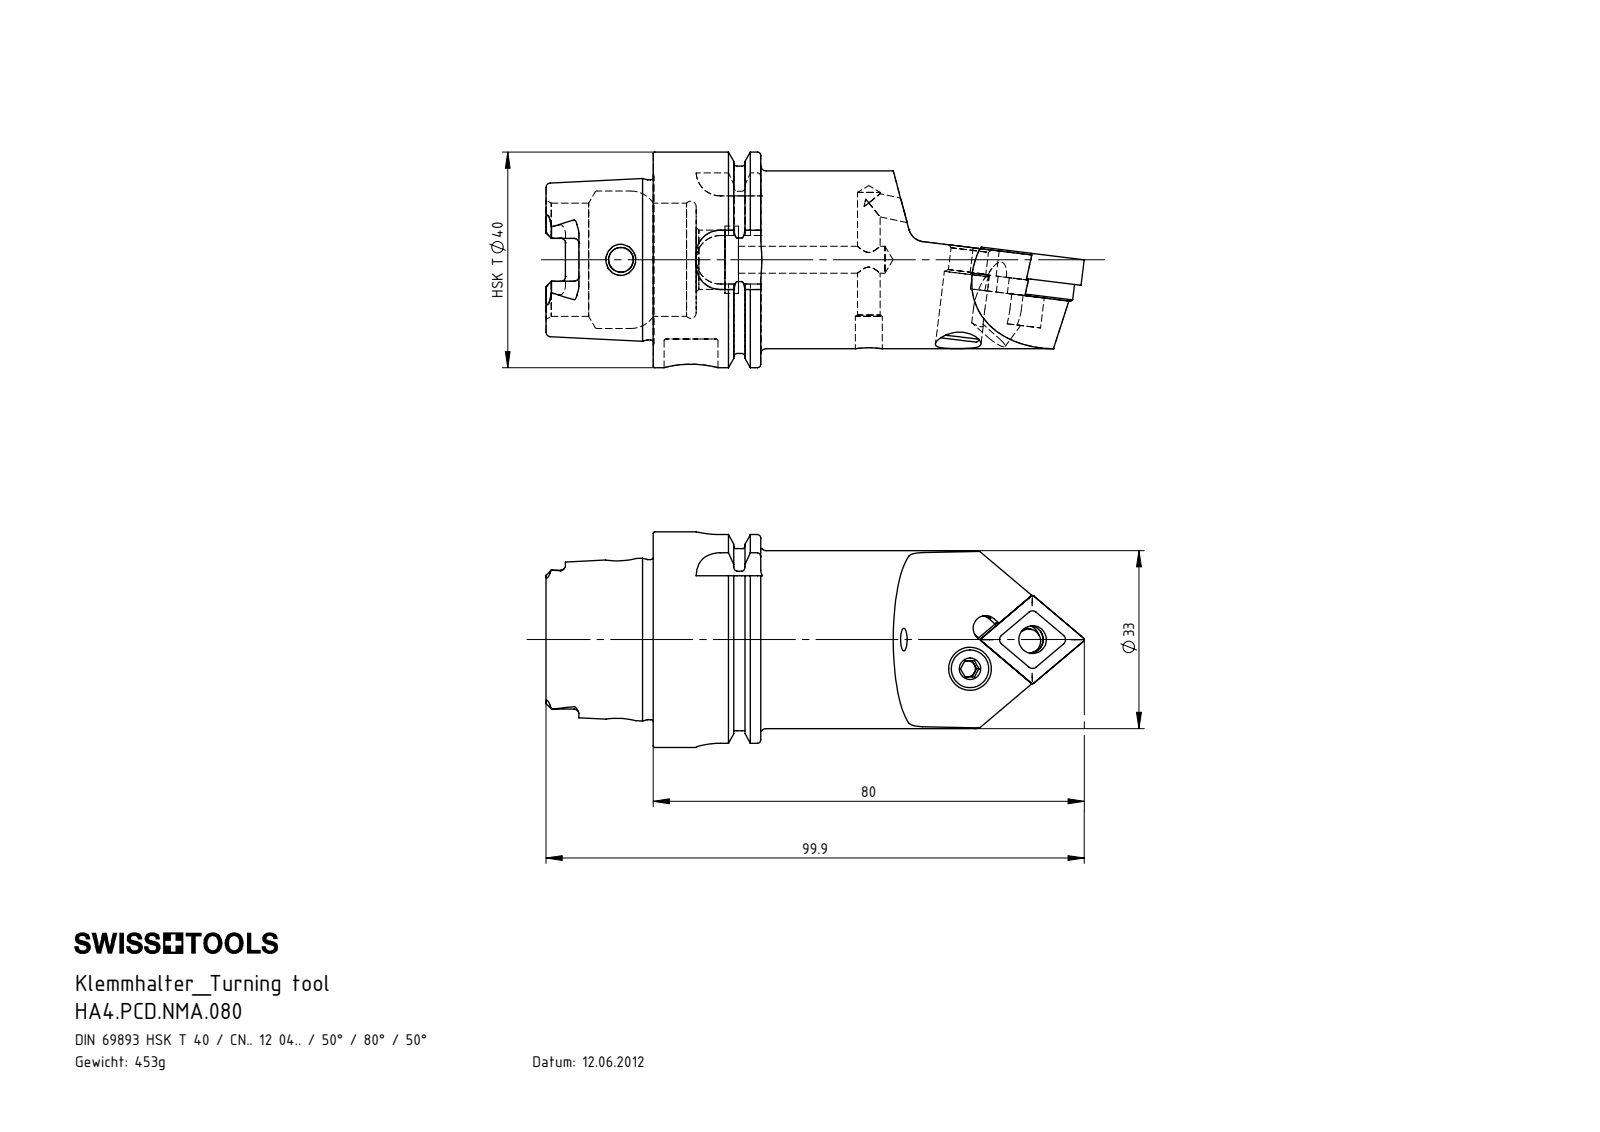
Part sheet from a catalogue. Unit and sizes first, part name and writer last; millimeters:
Units: millimetres
Overall size (bounding box): 99.9 × 40 × 40
Round holes (diameter × count): ⌀4.2 ×2, ⌀4 ×1, ⌀4.6 ×1, ⌀5 ×1, ⌀5.16 ×1, ⌀6.4 ×1, ⌀7 ×1, ⌀8.4 ×1, ⌀10 ×1, ⌀11 ×1, ⌀12.5 ×1, ⌀21 ×1
Round bosses / shafts (diameter × count): ⌀40 ×1, ⌀34.75 ×1, ⌀33 ×1, ⌀29.71 ×1, ⌀8 ×1, ⌀7.9 ×1, ⌀6.4 ×1, ⌀5 ×1
Partial cylindrical surfaces — rounded edges, fillets, slot ends (radius × count): R0.9 ×6, R0.4 ×4, R1 ×4, R1.88 ×4, R4.5 ×4, R2.5 ×2, R3.2 ×2, R0.8 ×1
Main face-to-face distances: 4.46, 7.95, 19.95, 12, 3.18, 7.64, 19.9, 27.85, 39.85, 12.7
Hole centre spacings: 12.8, 12.85, 28
Volume: 55 613 mm³ · Surface area: 17 674 mm²
Bodies: 8 solids, 293 faces (122 planar, 69 cylindrical, 102 other)
Part name (STEP PRODUCT): WCD-ER3.101.000_A; CNMG120404; KVT_MB_600_050; HA4-PCD.NMA.080 (+4 more)
STEP written by: SolidWorks 2017 (CONFIG_CONTROL_DESIGN)
